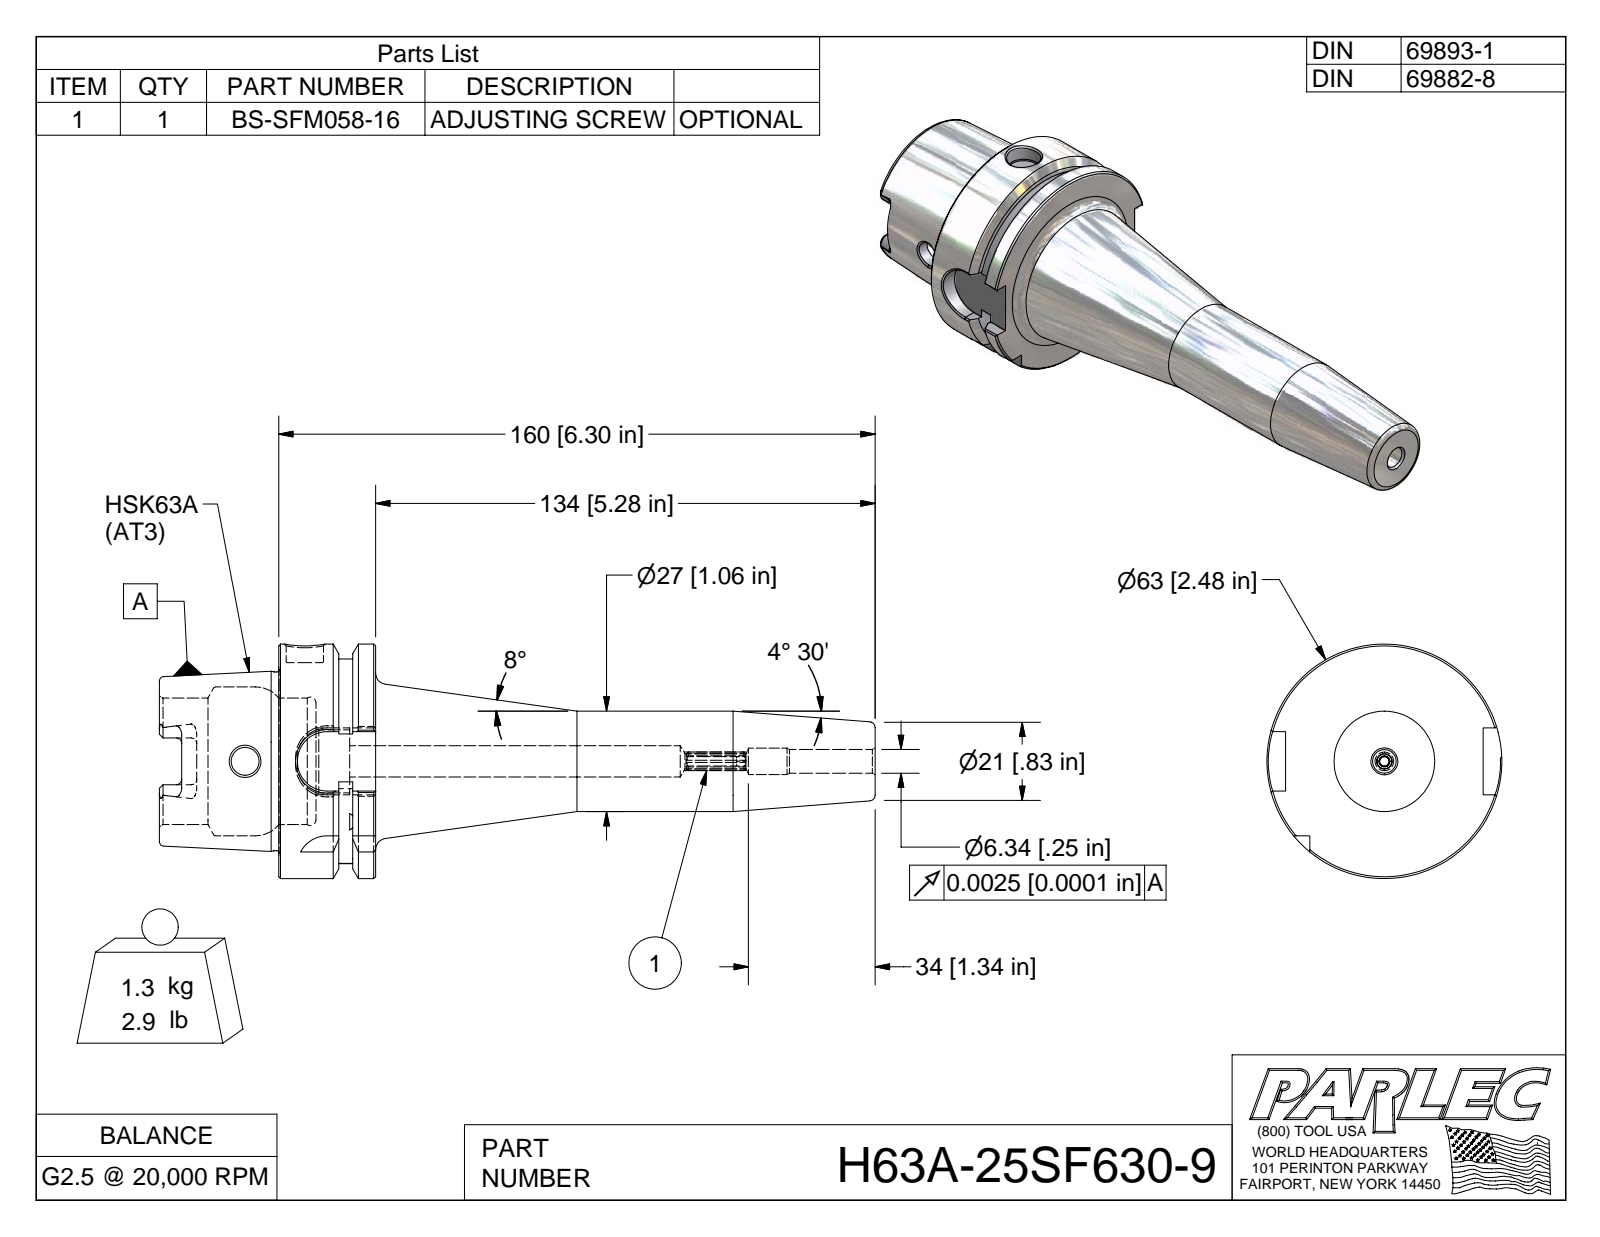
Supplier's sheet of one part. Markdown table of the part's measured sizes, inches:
| quantity | value |
| --- | --- |
| part name | H63A-25SF630-9; H63A-25SF630-9-1; BS-SFM058-16 |
| STEP written by | Autodesk Inventor 2009 (AUTOMOTIVE_DESIGN) |
| units | inches |
| bodies | 2 solids, 160 faces (59 planar, 35 cylindrical, 66 other) |
| overall size | 7.559 × 2.48 × 2.48 |
| volume | 10.31 in³ |
| surface area | 57.36 in² |
| round holes (diameter × count) | 0.25 × 1, 0.28 × 1, 0.295 × 1, 0.394 × 1, 0.666 × 1, 1.339 × 1, 1.575 × 1 |
| round bosses / shafts (diameter × count) | 2.48 × 1, 1.891 × 1, 1.063 × 1 |
| partial cylindrical surfaces (radius × count) | 0.059 × 6, 0.113 × 4, 0.315 × 4, 0.098 × 1, 1.083 × 1 |
| main face-to-face distances | 1.024, 0.241, 0.389, 0.394, 0.63, 1.26, 1.654, 2.283, 1.894, 0.635 |
